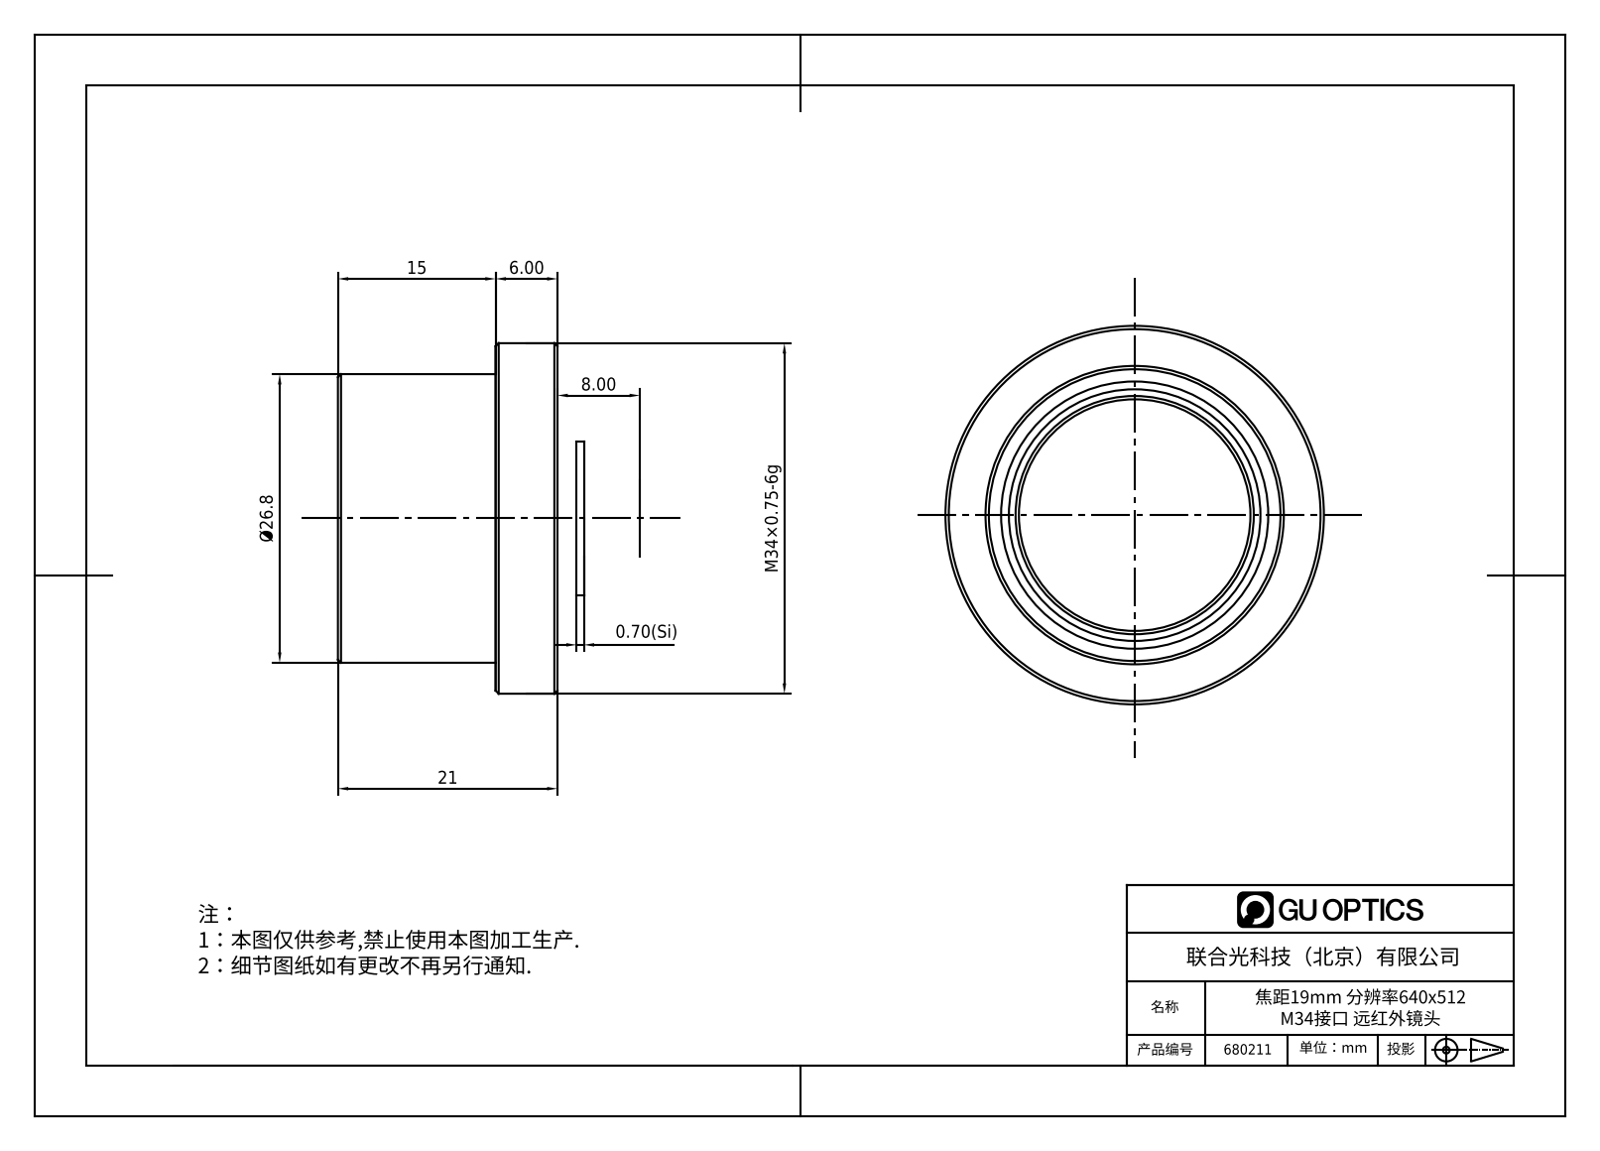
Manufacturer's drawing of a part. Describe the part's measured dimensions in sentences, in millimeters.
The part is named "19mm". Its 3-D file was written by "SolidWorks 2020 (CONFIG_CONTROL_DESIGN)". It is 1 solid with 20 faces: 5 planar, 6 cylindrical and 9 other. Overall it measures 34 by 34 by 21 millimeters. Its volume is 12 417 cubic millimeters and its surface area 4 099 square millimeters. Round holes: 1 of diameter 17.4, 1 of diameter 22.6, 1 of diameter 23.4. Round bosses or shafts: 1 of diameter 34, 1 of diameter 26.8, 1 of diameter 21.4. The main face-to-face distances are 6, 15, 21, 2.3, 12.7, 18.7, 3.3, 1, 11.7, 17.7.
